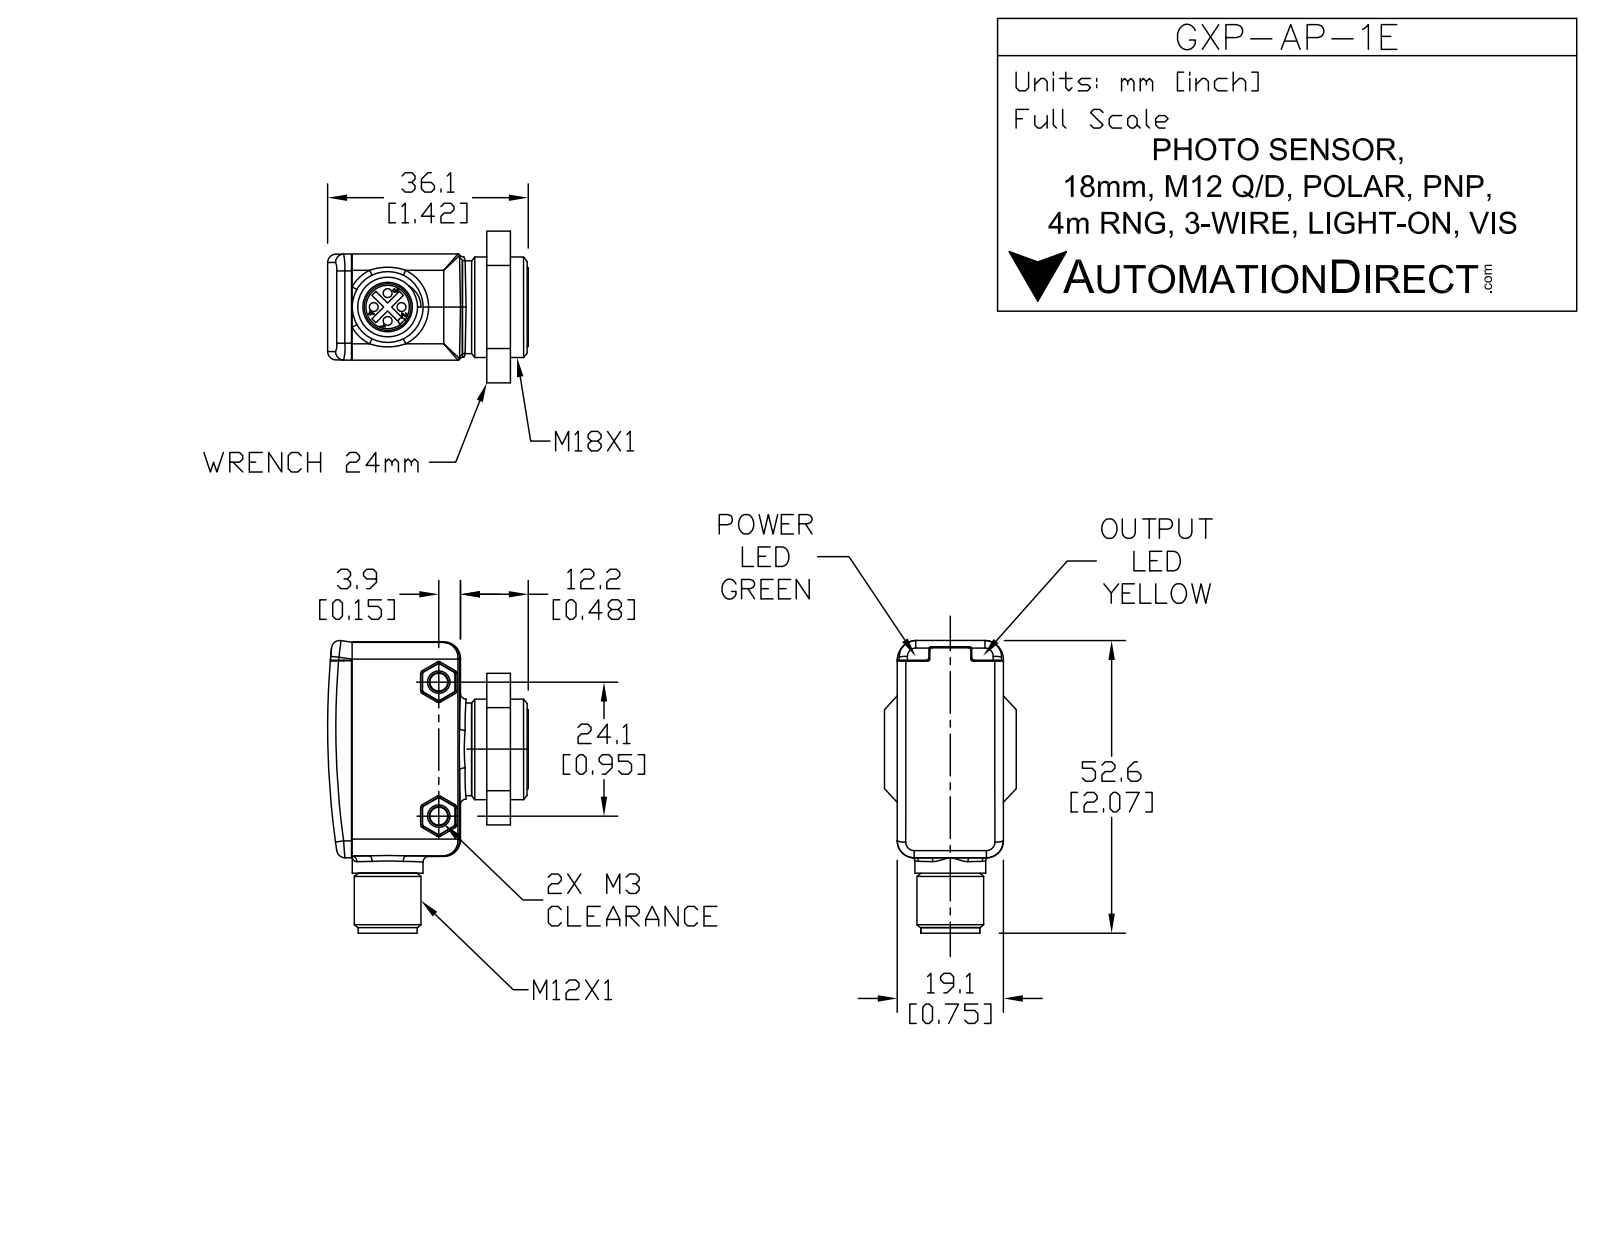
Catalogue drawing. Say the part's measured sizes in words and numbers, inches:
The part is named "GXP-AP-1E". Its 3-D file was written by "SolidWorks 2013 (AUTOMOTIVE_DESIGN)". It is 1 solid with 107 faces: 60 planar, 33 cylindrical and 14 other. Overall it measures 2.073 by 1.421 by 0.939 inches. Its volume is 1.297 cubic inches and its surface area 10 square inches. Round holes: 2 of diameter 0.126, 1 of diameter 0.329. Round bosses or shafts: 1 of diameter 0.709, 1 of diameter 0.689, 1 of diameter 0.559, 1 of diameter 0.499, 1 of diameter 0.455, 1 of diameter 0.417. Partial cylindrical surfaces (rounded edges, fillets, slot ends): 8 of radius 0.059, 4 of radius 0.039, 1 of radius 5.495. The main face-to-face distances are 0.752, 0.283, 0.083, 0.367, 0.756, 0.197, 0.113, 0.48, 1.528, 0.234. The hole center spacings are 0.949.
